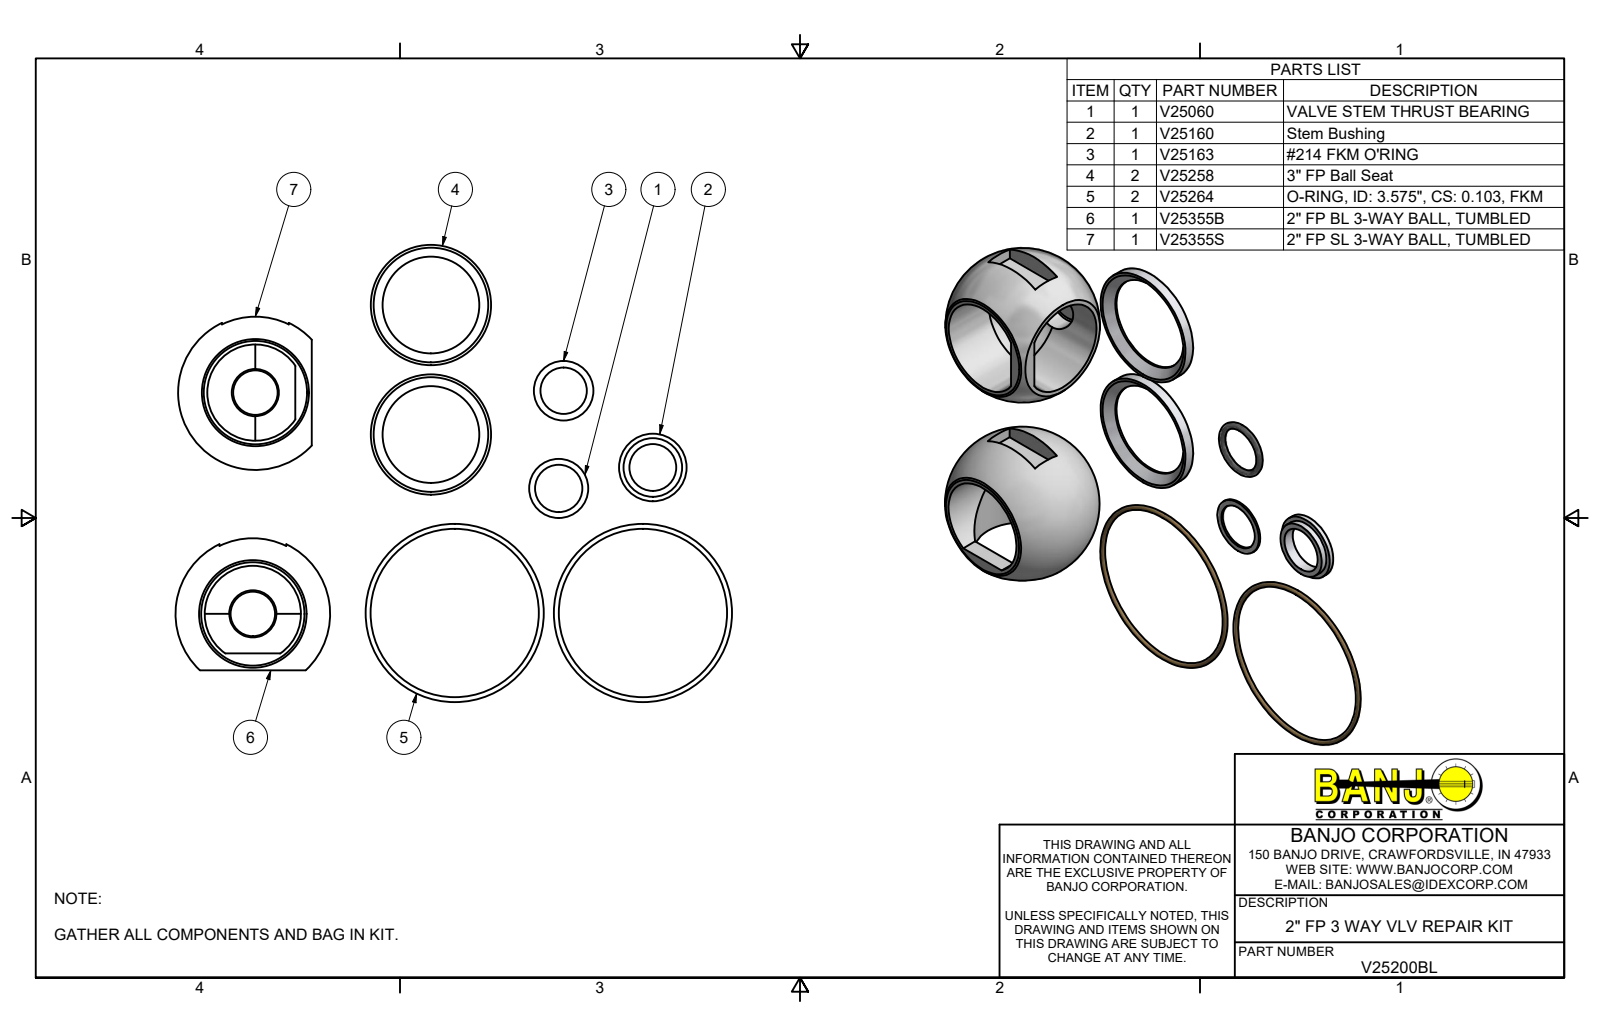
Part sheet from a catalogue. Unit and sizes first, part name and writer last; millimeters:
Units: millimetres
Overall size (bounding box): 300.3 × 246.5 × 73.2
Round holes (diameter × count): ⌀25.4 ×4, ⌀51.8 ×4, ⌀52.1 ×2
Round bosses / shafts (diameter × count): ⌀64.8 ×2, ⌀36.5 ×1, ⌀31.8 ×1, ⌀31.5 ×1
Main face-to-face distances: 1, 25.5, 42.1, 16.6, 5.8, 119.4, 32.1, 61.4, 180.8, 1.4
Hole centre spacings: 52, 69.9, 74.9, 97.4, 105.9, 119.4, 120.6, 121.1
Volume: 299 700 mm³ · Surface area: 73 160 mm²
Bodies: 9 solids, 69 faces (33 planar, 15 cylindrical, 21 other)
Part name (STEP PRODUCT): V25200BL; V25355B; V25355BM; VX25355B (+8 more)
STEP written by: Autodesk Inventor 2019 (AUTOMOTIVE_DESIGN)
